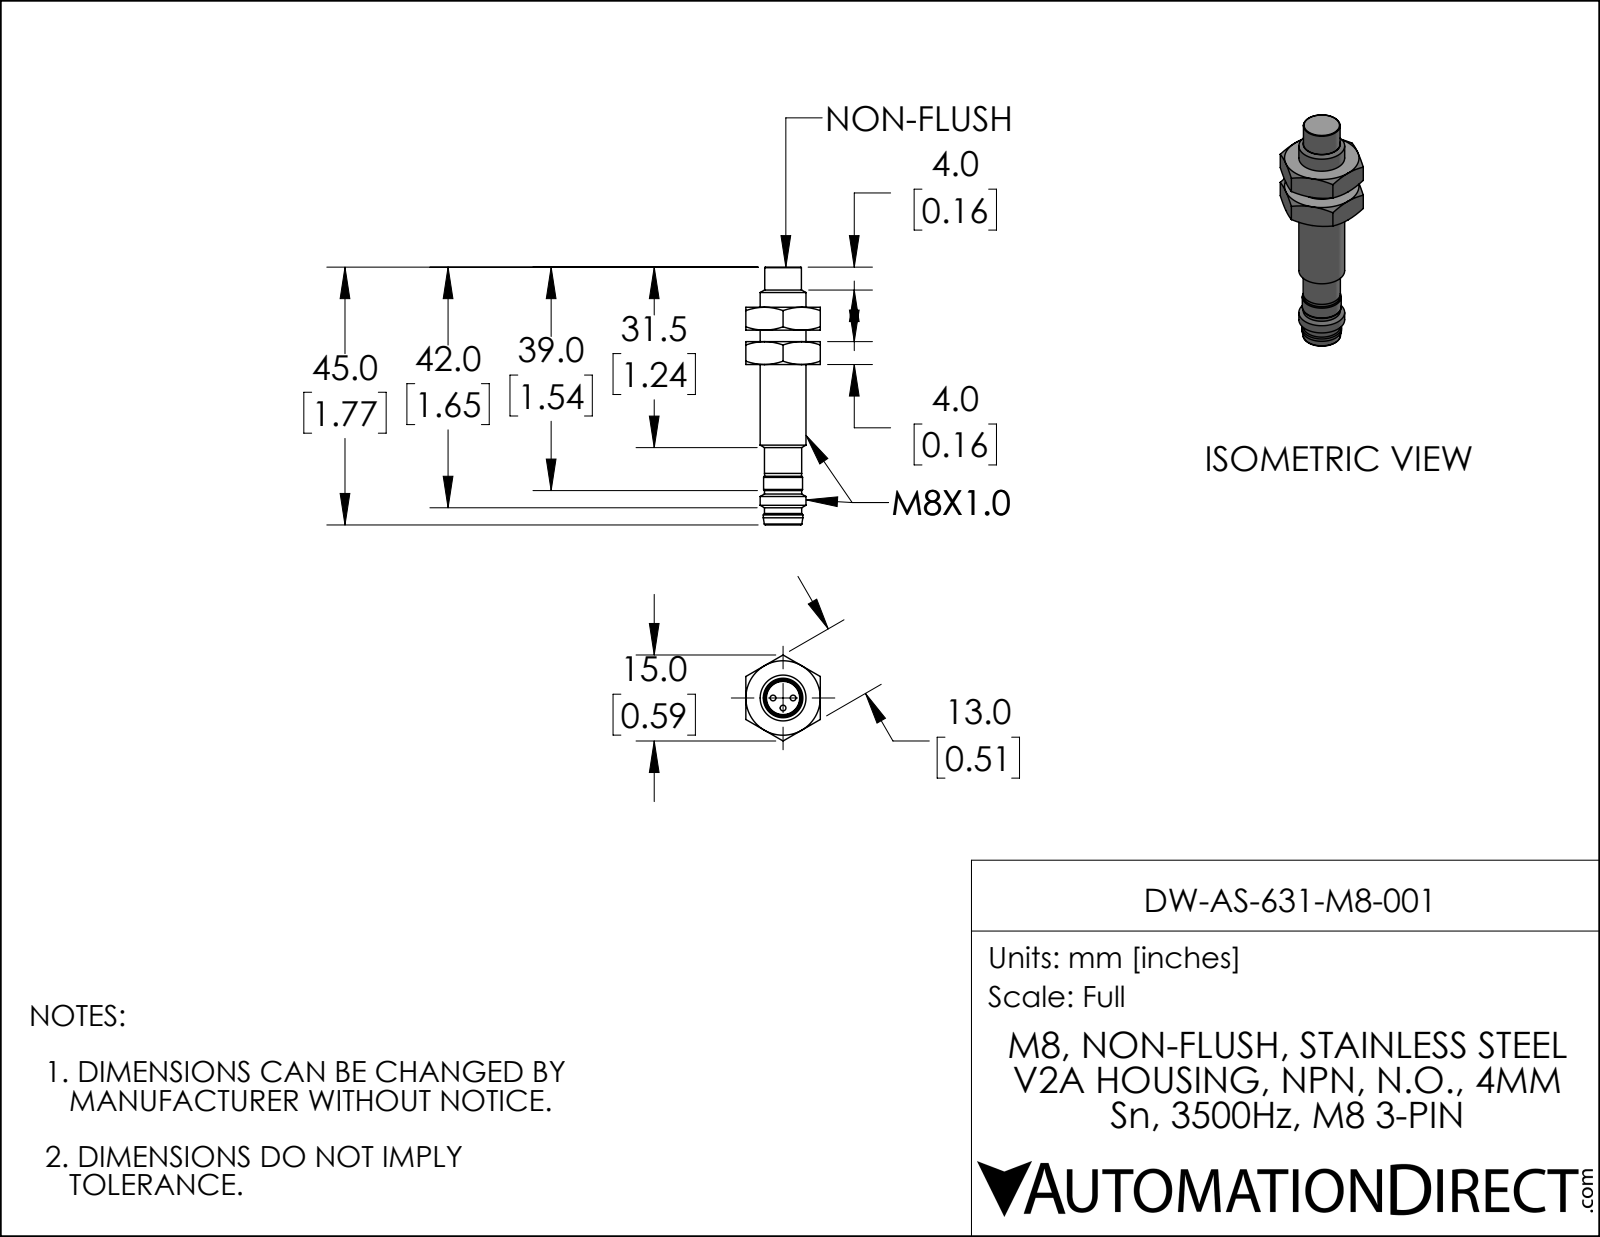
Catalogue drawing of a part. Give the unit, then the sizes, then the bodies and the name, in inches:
Units: inches
Overall size (bounding box): 1.772 × 0.591 × 0.512
Round holes (diameter × count): ⌀0.228 ×1
Round bosses / shafts (diameter × count): ⌀0.039 ×3, ⌀0.315 ×1, ⌀0.272 ×1, ⌀0.268 ×1, ⌀0.256 ×1, ⌀0.254 ×1, ⌀0.252 ×1
Main face-to-face distances: 0.512, 0.157, 0.236, 0.079, 0.394, 0.276, 0.433, 0.669, 1.142, 0.906
Volume: 0.161 in³ · Surface area: 2.817 in²
Bodies: 1 solid, 76 faces (24 planar, 15 cylindrical, 37 other)
Part name (STEP PRODUCT): DW-AS-631-M8-001
STEP written by: SolidWorks 2019 (AUTOMOTIVE_DESIGN)
